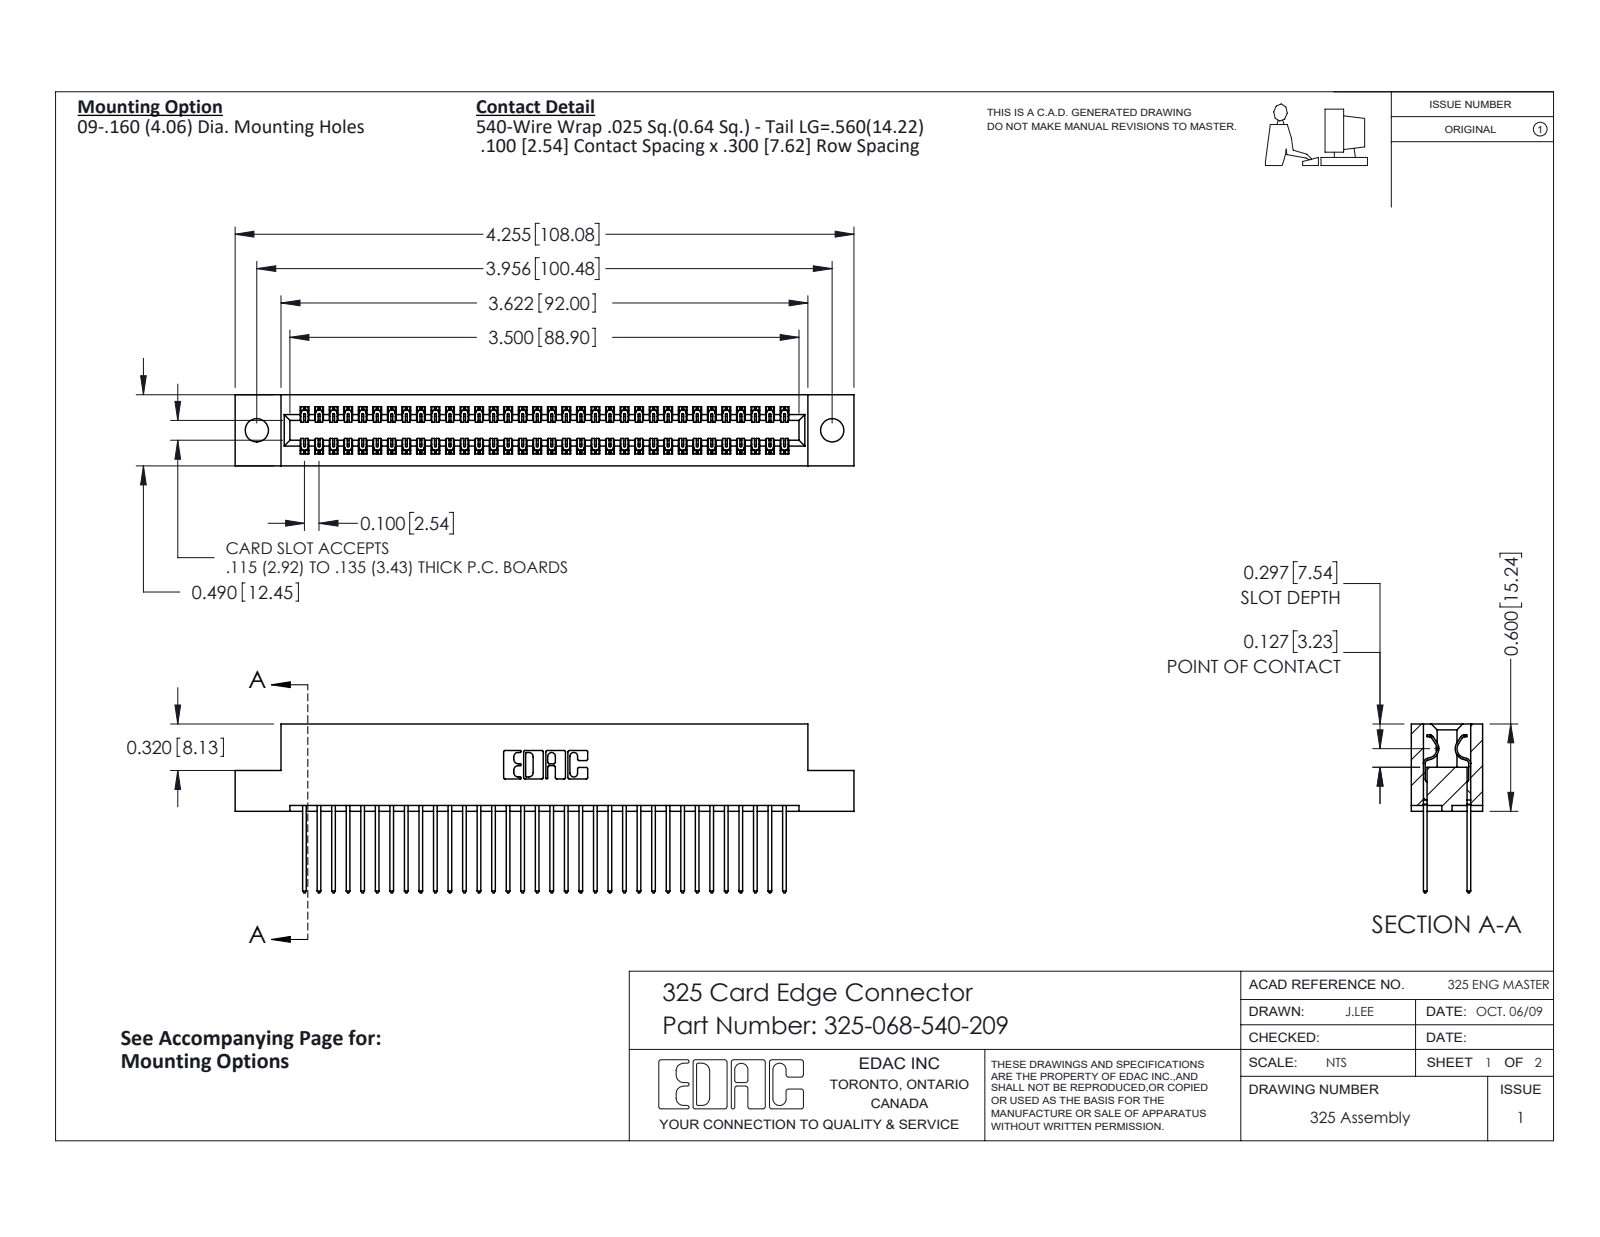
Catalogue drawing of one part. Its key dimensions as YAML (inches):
part_name: "325-068-540-209; 325 Part_.160 TH; 325-292-001_325-293-140"
step_written_by: "SolidWorks 2016 (CONFIG_CONTROL_DESIGN)"
units: inches
bodies: {solids: 69, faces: 3650, planar: 2518, cylindrical: 1132, other: 0}
overall_size: [4.255, 1.16, 0.49]
volume: 0.849
surface_area: 27.58
round_holes:
  - {diameter: 0.16, count: 2}
partial_cylinders:
  - {radius: 0.006, count: 102}
  - {radius: 0.01, count: 68}
  - {radius: 0.01, count: 22}
  - {radius: 0.007, count: 6}
  - {radius: 0.031, count: 6}
  - {radius: 0.026, count: 3}
  - {radius: 0.014, count: 2}
  - {radius: 0.022, count: 2}
face_to_face_distances: [0.083, 0.407, 0.3, 0.107, 0.383, 0.025, 0.49, 0.325, 0.275, 0.04]
hole_center_spacings: [3.956]
